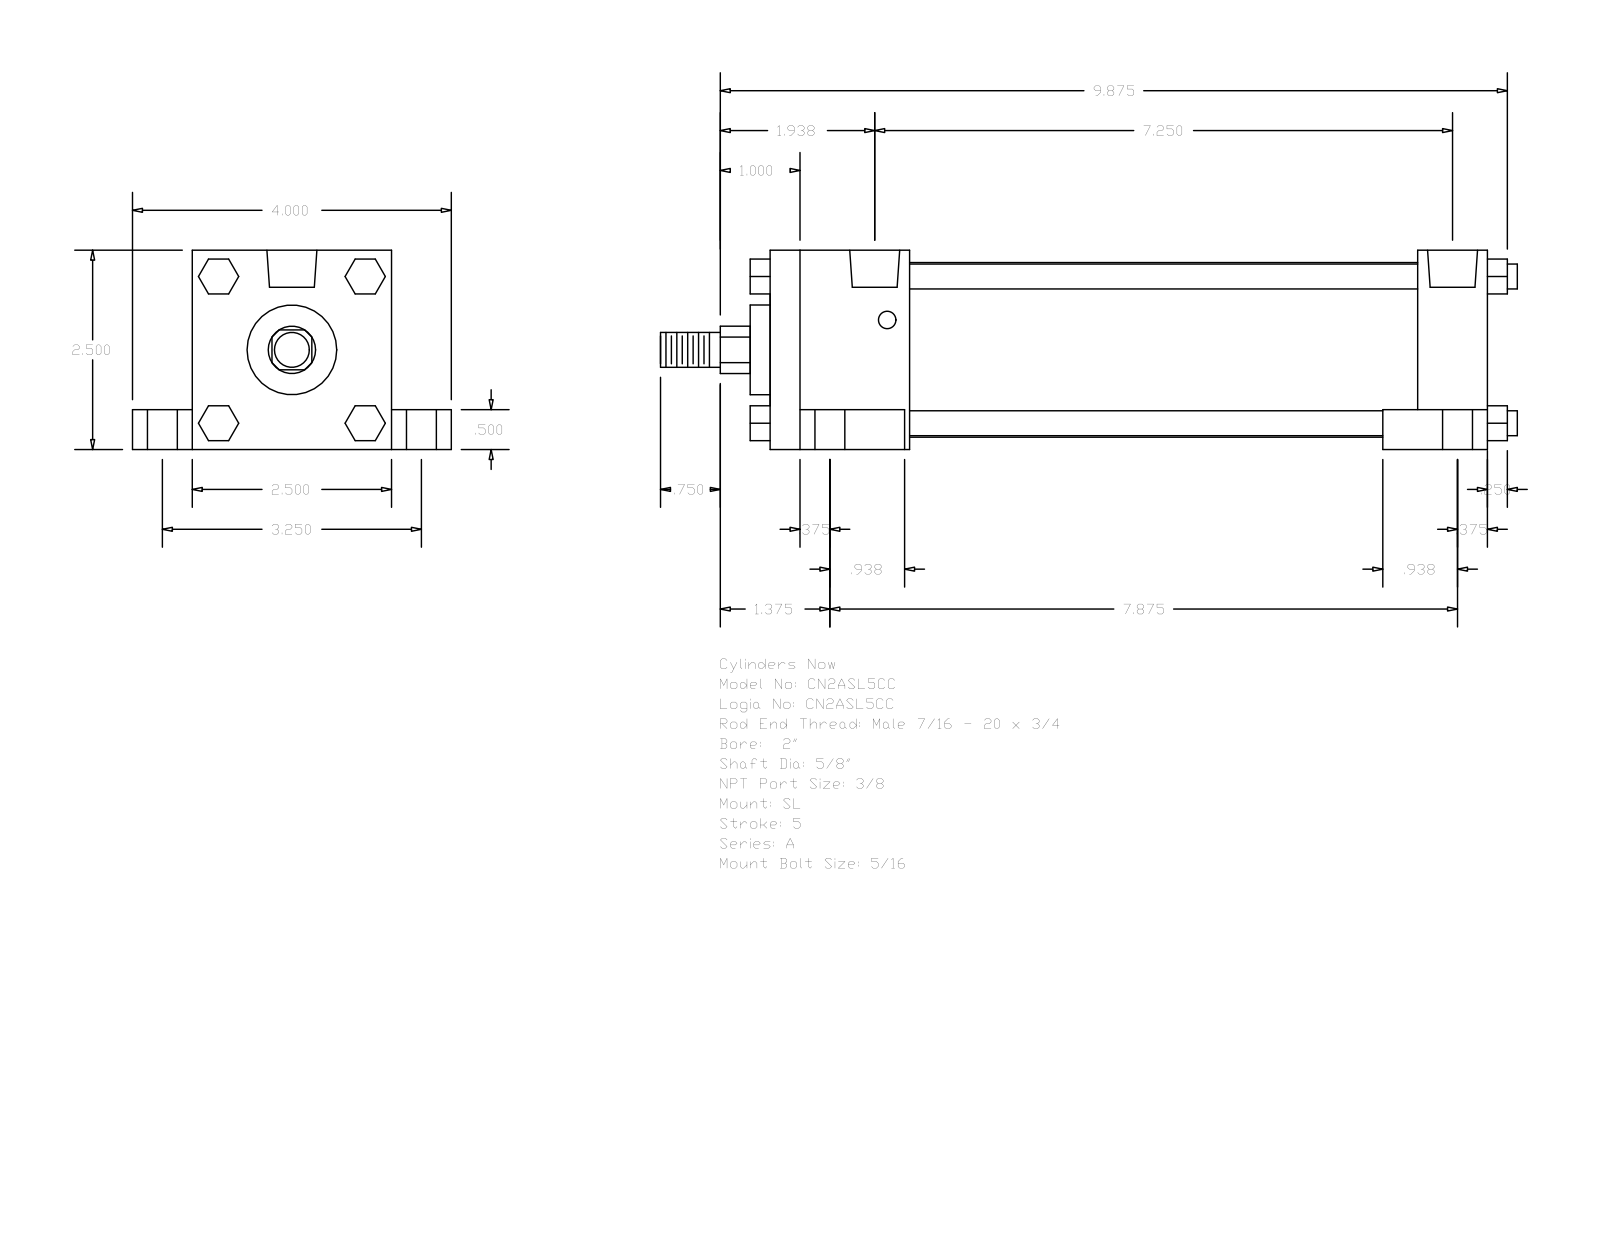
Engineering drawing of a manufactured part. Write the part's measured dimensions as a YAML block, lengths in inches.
part_name: "A_SL__0200_0.625"
step_written_by: "GSSL Pune (CONFIG_CONTROL_DESIGN)"
units: inches
bodies: {solids: 0, faces: 148, planar: 112, cylindrical: 36, other: 0}
overall_size: [10.75, 4, 2.5]
round_holes:
  - {diameter: 0.219, count: 4}
  - {diameter: 0.375, count: 4}
  - {diameter: 0.625, count: 4}
  - {diameter: 0.627, count: 2}
round_bosses_or_shafts:
  - {diameter: 0.313, count: 4}
  - {diameter: 2.19, count: 1}
  - {diameter: 1.125, count: 1}
  - {diameter: 0.625, count: 1}
  - {diameter: 0.437, count: 1}
partial_cylinders:
  - {radius: 0.297, count: 1}
face_to_face_distances: [2.5, 9, 2, 0.5, 0.75, 3.25, 1.75, 7.25, 8.125, 6.375]
hole_center_spacings: [1.626, 1.639, 1.719, 1.777, 3.25, 6.937, 7.338, 7.491]
